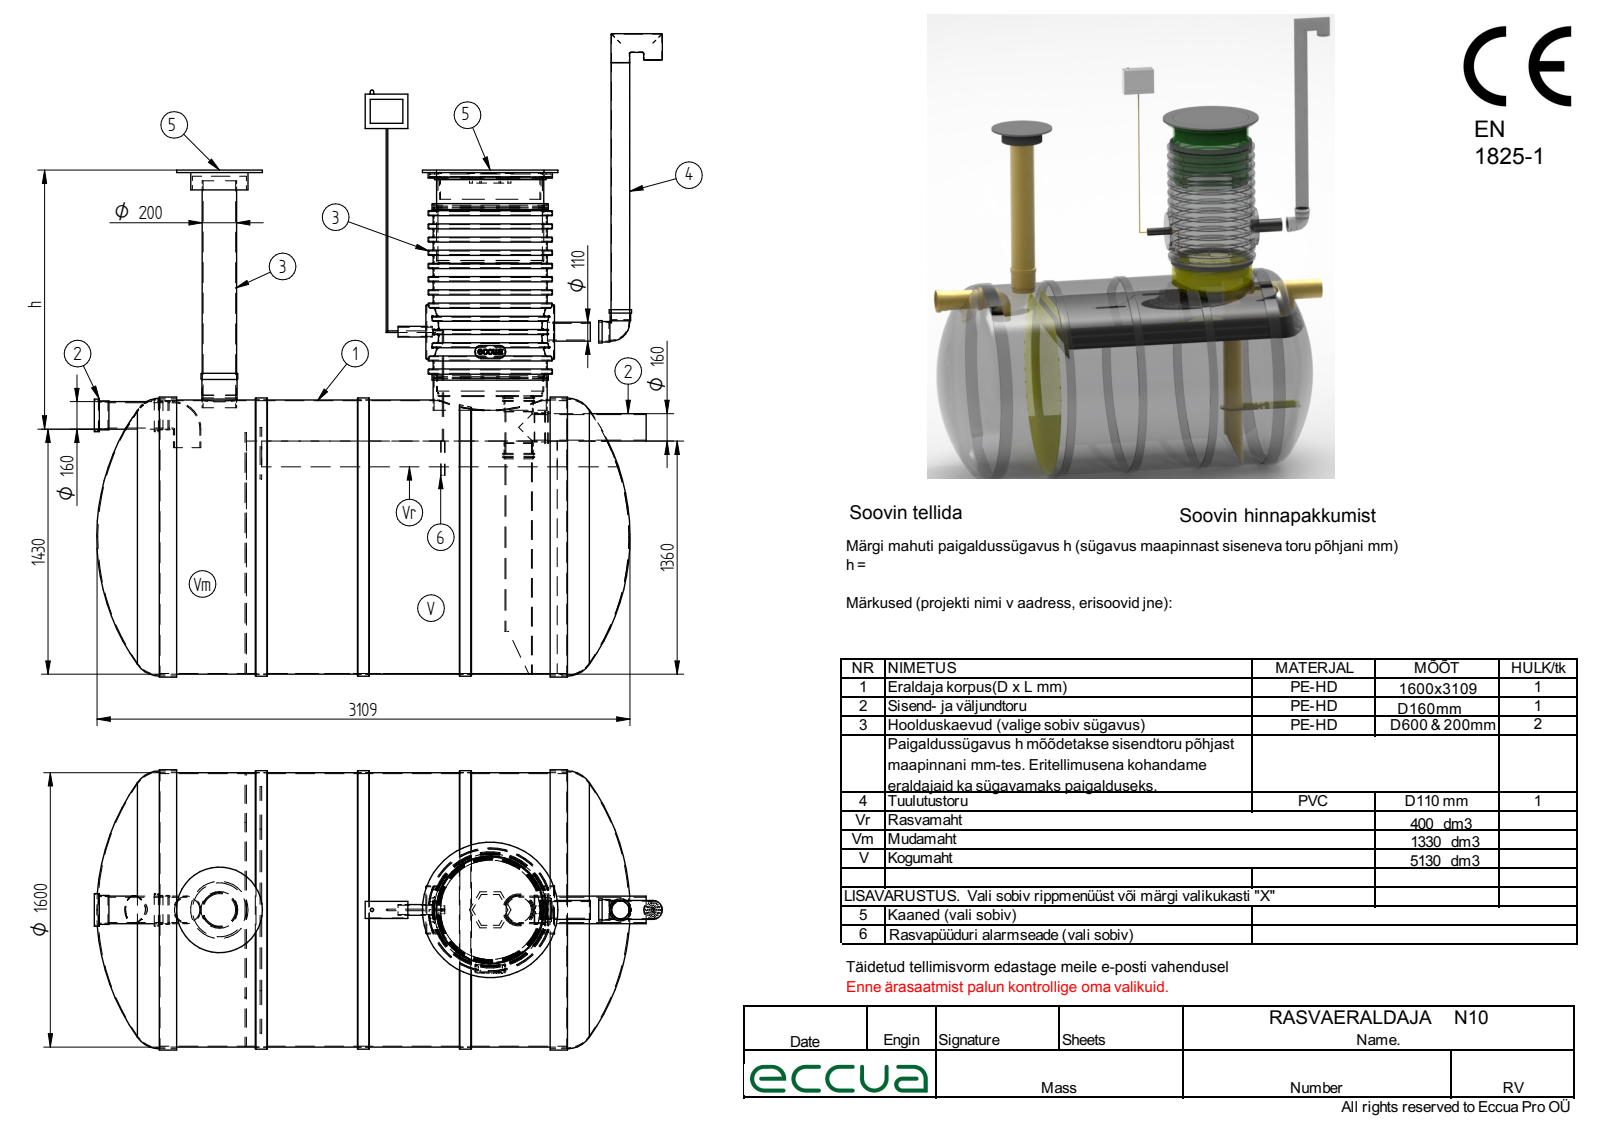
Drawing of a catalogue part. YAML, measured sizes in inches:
part_name: "NS10 Rasvaeraldaja 2023; 2259.013; 2259.002; 2259.014 (+8 more)"
step_written_by: "Solid Edge (AUTOMOTIVE_DESIGN)"
units: inches
bodies: {solids: 40, faces: 776, planar: 305, cylindrical: 265, other: 206}
overall_size: [165.9, 130.483, 100.591]
volume: 881200
surface_area: 237800
round_holes:
  - {diameter: 0.394, count: 31}
  - {diameter: 5.827, count: 4}
  - {diameter: 4.063, count: 3}
  - {diameter: 6.299, count: 3}
  - {diameter: 3.937, count: 2}
  - {diameter: 6.85, count: 2}
  - {diameter: 0.236, count: 1}
  - {diameter: 0.803, count: 1}
  - {diameter: 2.11, count: 1}
  - {diameter: 3.811, count: 1}
  - {diameter: 4.134, count: 1}
  - {diameter: 6.142, count: 1}
round_bosses_or_shafts:
  - {diameter: 4.331, count: 4}
  - {diameter: 0.335, count: 3}
  - {diameter: 7.323, count: 2}
  - {diameter: 6.693, count: 2}
  - {diameter: 6.299, count: 2}
  - {diameter: 5.118, count: 2}
  - {diameter: 4.724, count: 2}
  - {diameter: 64.33, count: 1}
partial_cylinders:
  - {radius: 0.118, count: 4}
  - {radius: 0.197, count: 4}
  - {radius: 1.181, count: 4}
  - {radius: 1.378, count: 4}
  - {radius: 5.315, count: 2}
  - {radius: 5.512, count: 2}
  - {radius: 4.331, count: 1}
  - {radius: 9.587, count: 1}
face_to_face_distances: [0.315, 5.906, 3.465, 7.874, 1.969, 68.122, 62.216, 60.248, 0.197, 3.78]
hole_center_spacings: [1.575, 1.964, 2.838, 1.367, 2.463, 1.053, 0.531, 3.071]
